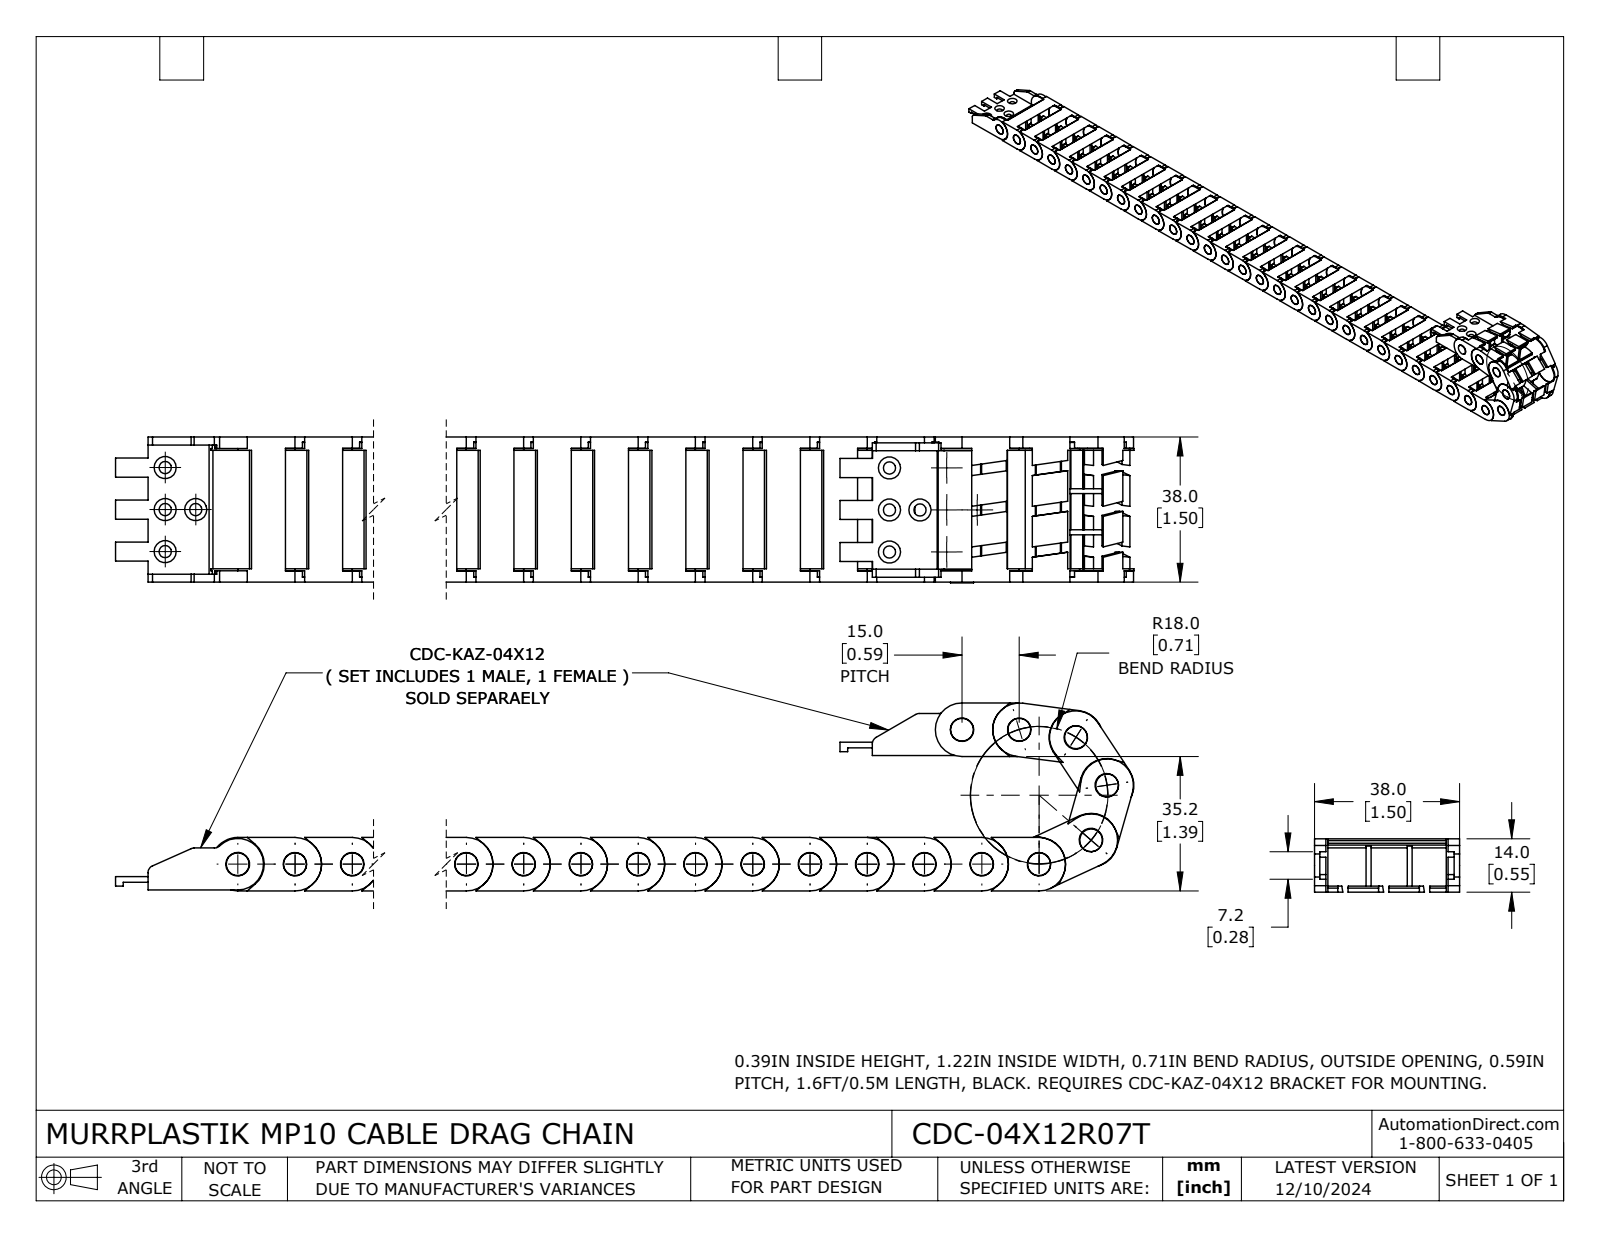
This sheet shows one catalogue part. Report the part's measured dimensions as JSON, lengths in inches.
{"part_name": "CDC-04X12R07T", "step_written_by": "SolidWorks 2024 (AUTOMOTIVE_DESIGN)", "units": "inches", "bodies": {"solids": 34, "faces": 3106, "planar": 2224, "cylindrical": 874, "other": 8}, "overall_size": [18.773, 1.937, 1.504], "volume_in3": 5, "surface_area_in2": 179.4, "round_holes": [[0.242, 32], [0.126, 8], [0.244, 1]], "round_bosses_or_shafts": [[0.236, 33], [0.551, 28]], "partial_cylinders_radius": [[0.02, 160], [0.274, 36], [0.142, 32], [0.457, 32], [0.276, 8], [0.079, 6], [0.039, 2], [0.266, 2]], "face_to_face_distances": [0.138, 1.358, 0.051, 0.551, 0.063, 1.496, 1.22, 1.307, 0.087, 1.445], "hole_center_spacings": [0.591, 1.181, 1.772, 2.362, 2.953, 3.543, 4.134, 4.724]}
